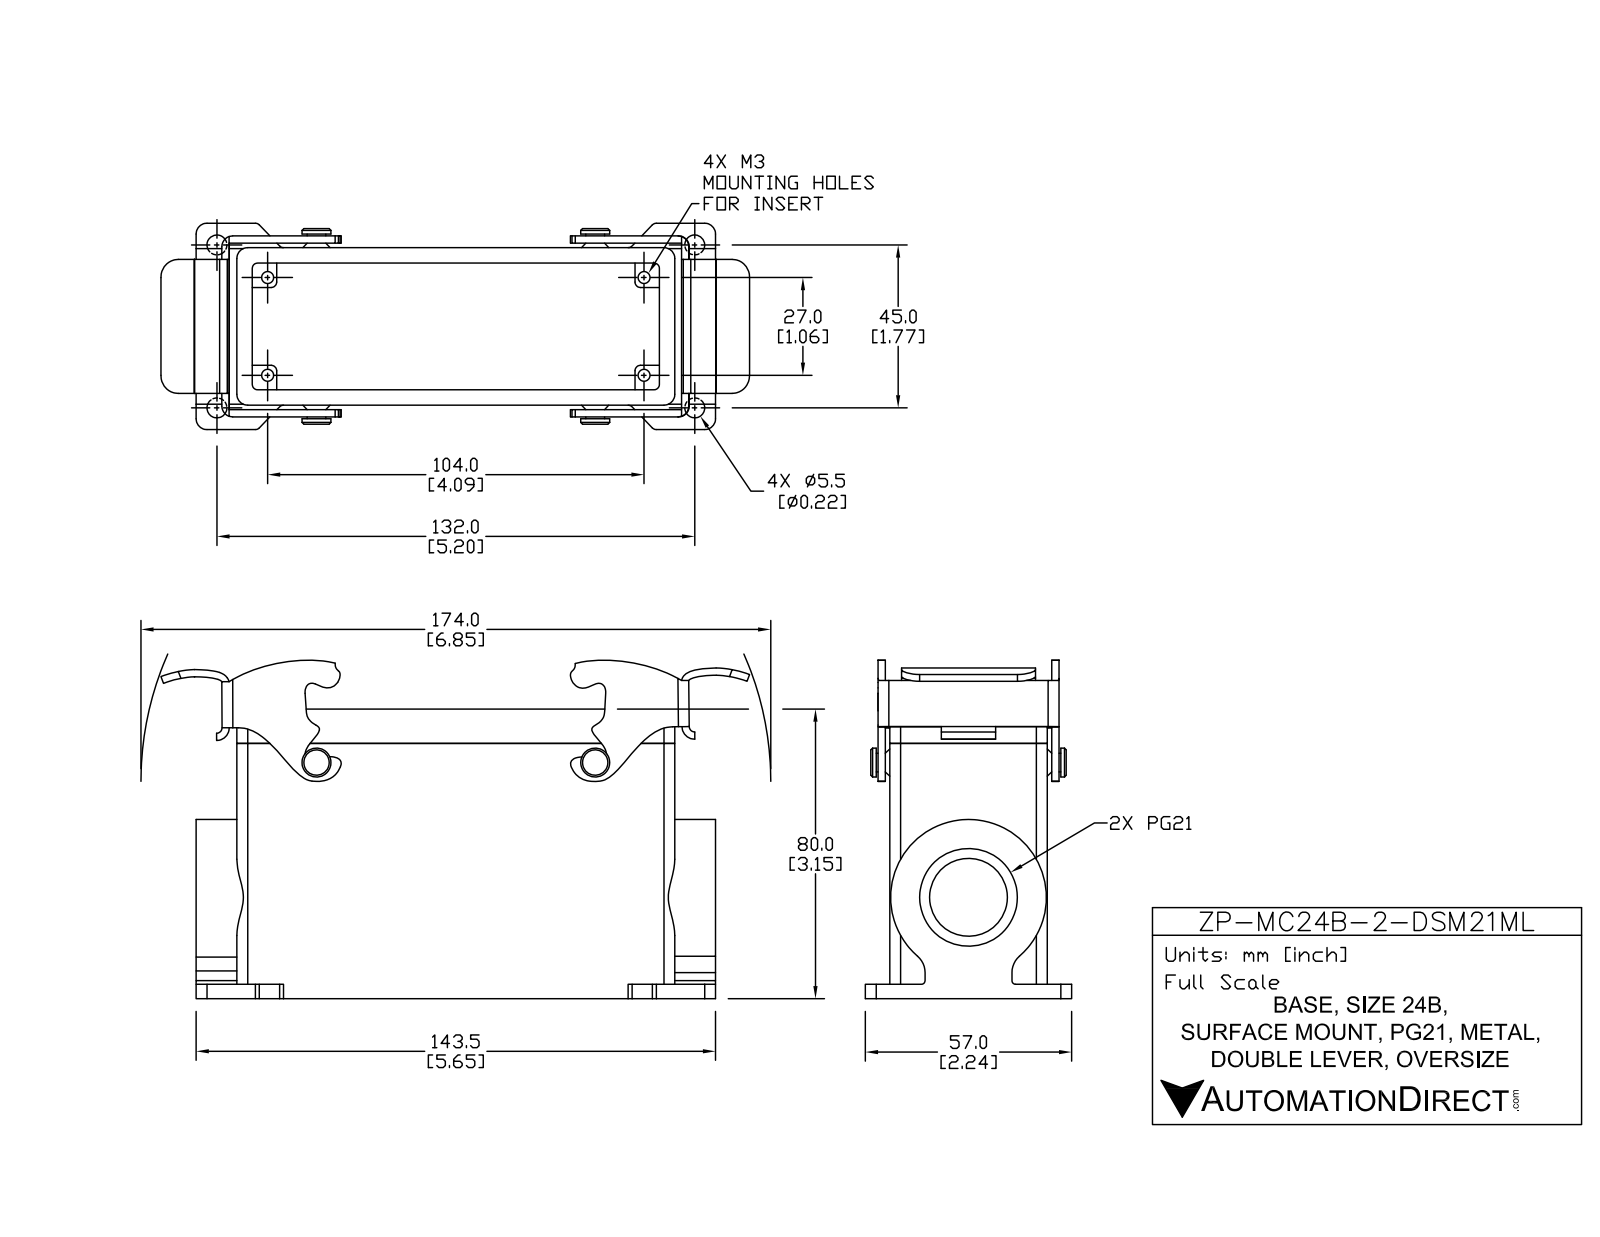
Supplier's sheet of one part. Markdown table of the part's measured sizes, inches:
| quantity | value |
| --- | --- |
| part name | ZP-MC24B-2-DSM21ML |
| STEP written by | SolidWorks 2011 (AUTOMOTIVE_DESIGN) |
| units | inches |
| bodies | 4 solids, 321 faces (131 planar, 182 cylindrical, 8 other) |
| overall size | 6.798 × 3.57 × 2.244 |
| volume | 9.541 in³ |
| surface area | 125.1 in² |
| round holes (diameter × count) | 0.13 × 4, 0.217 × 4, 0.846 × 1, 1.063 × 1 |
| round bosses / shafts (diameter × count) | 0.315 × 2, 0.204 × 2 |
| partial cylindrical surfaces (radius × count) | 0.02 × 26, 0.059 × 16, 0.118 × 10, 0.039 × 6, 0.079 × 6, 0.157 × 6, 0.197 × 4, 0.394 × 4 |
| main face-to-face distances | 0.167, 1.545, 1.713, 1.378, 0.098, 0.045, 0.433, 0.266, 4.596, 2.776 |
| hole center spacings | 0.655, 1.521, 4.659, 4.857, 1.063, 1.772, 4.094, 4.23 |
